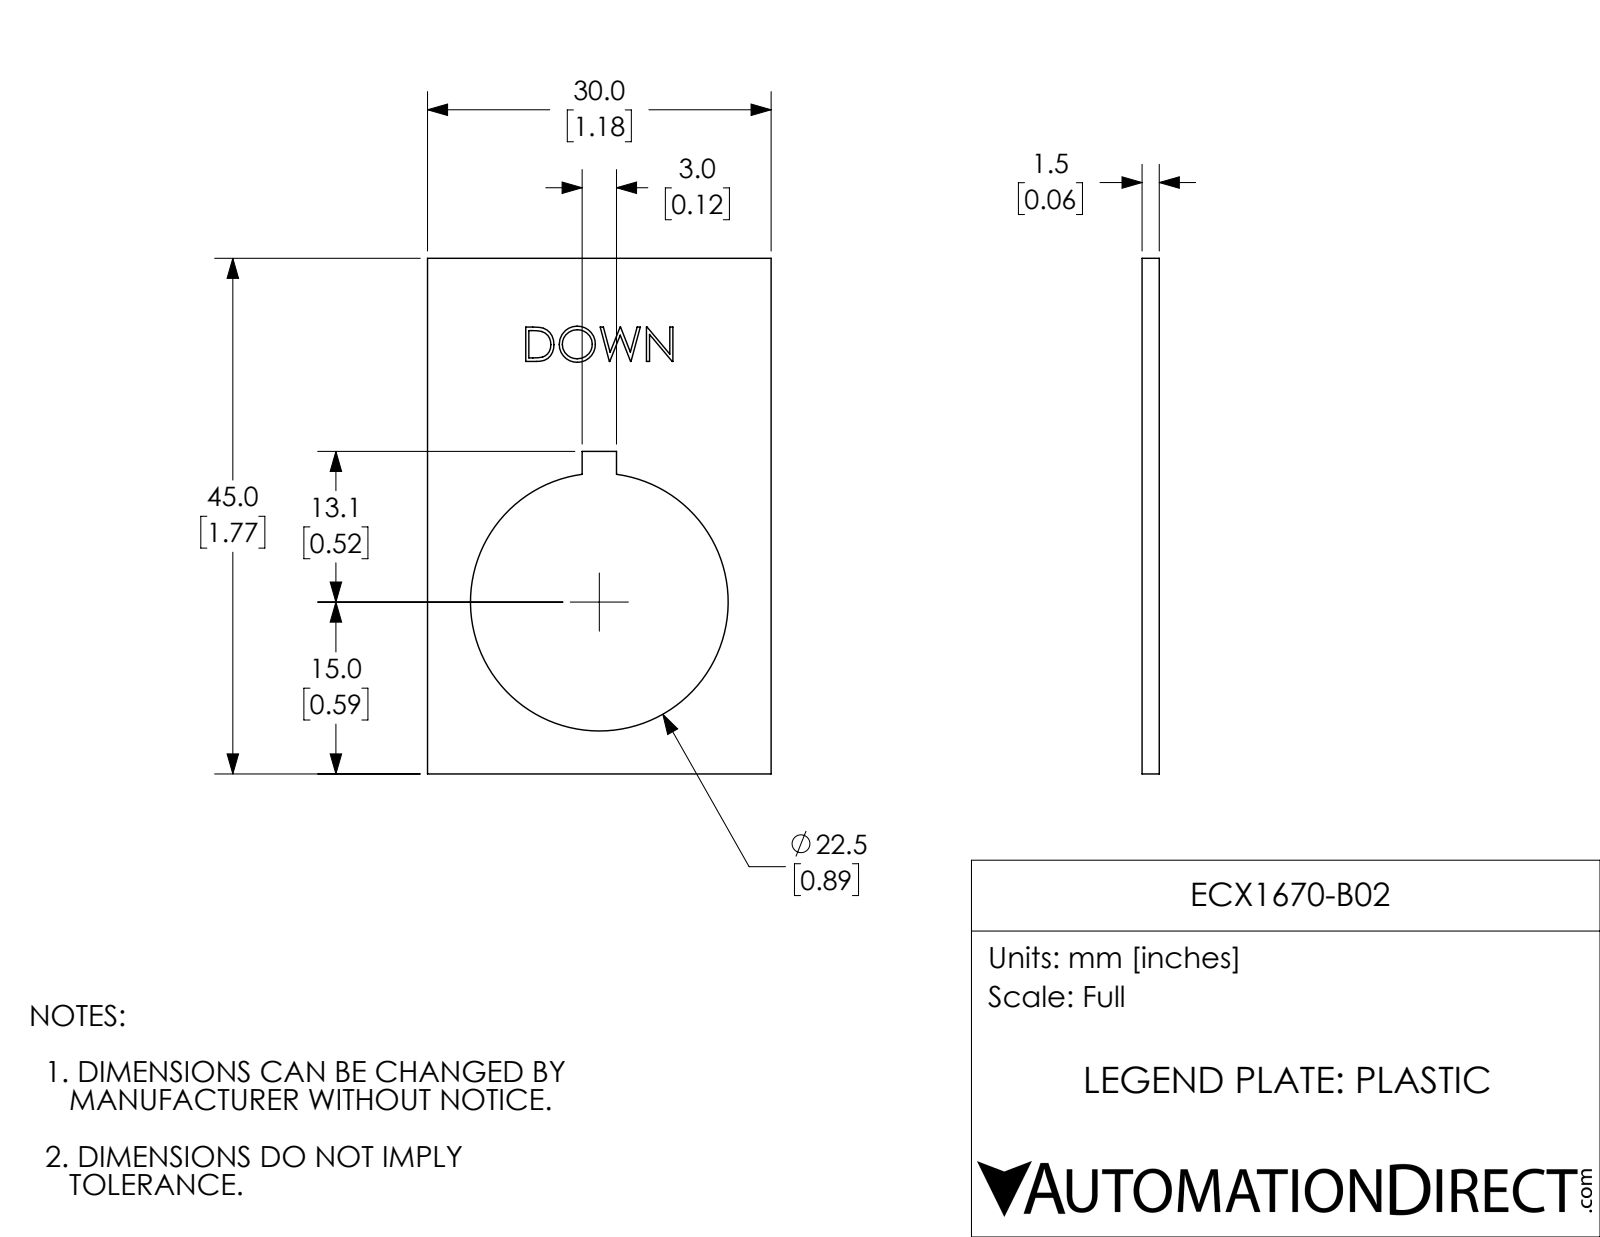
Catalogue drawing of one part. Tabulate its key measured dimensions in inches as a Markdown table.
| quantity | value |
| --- | --- |
| part name | ECX1670-B02 |
| STEP written by | SolidWorks 2017 (AUTOMOTIVE_DESIGN) |
| units | inches |
| bodies | 1 solid, 62 faces (44 planar, 3 cylindrical, 15 other) |
| overall size | 1.772 × 1.181 × 0.059 |
| volume | 0.087 in³ |
| surface area | 3.46 in² |
| round holes (diameter × count) | 0.886 × 1 |
| main face-to-face distances | 0.059, 1.181, 1.772, 0.058, 0.531, 0.65, 1.108, 0.663, 0.118, 0.338 |
